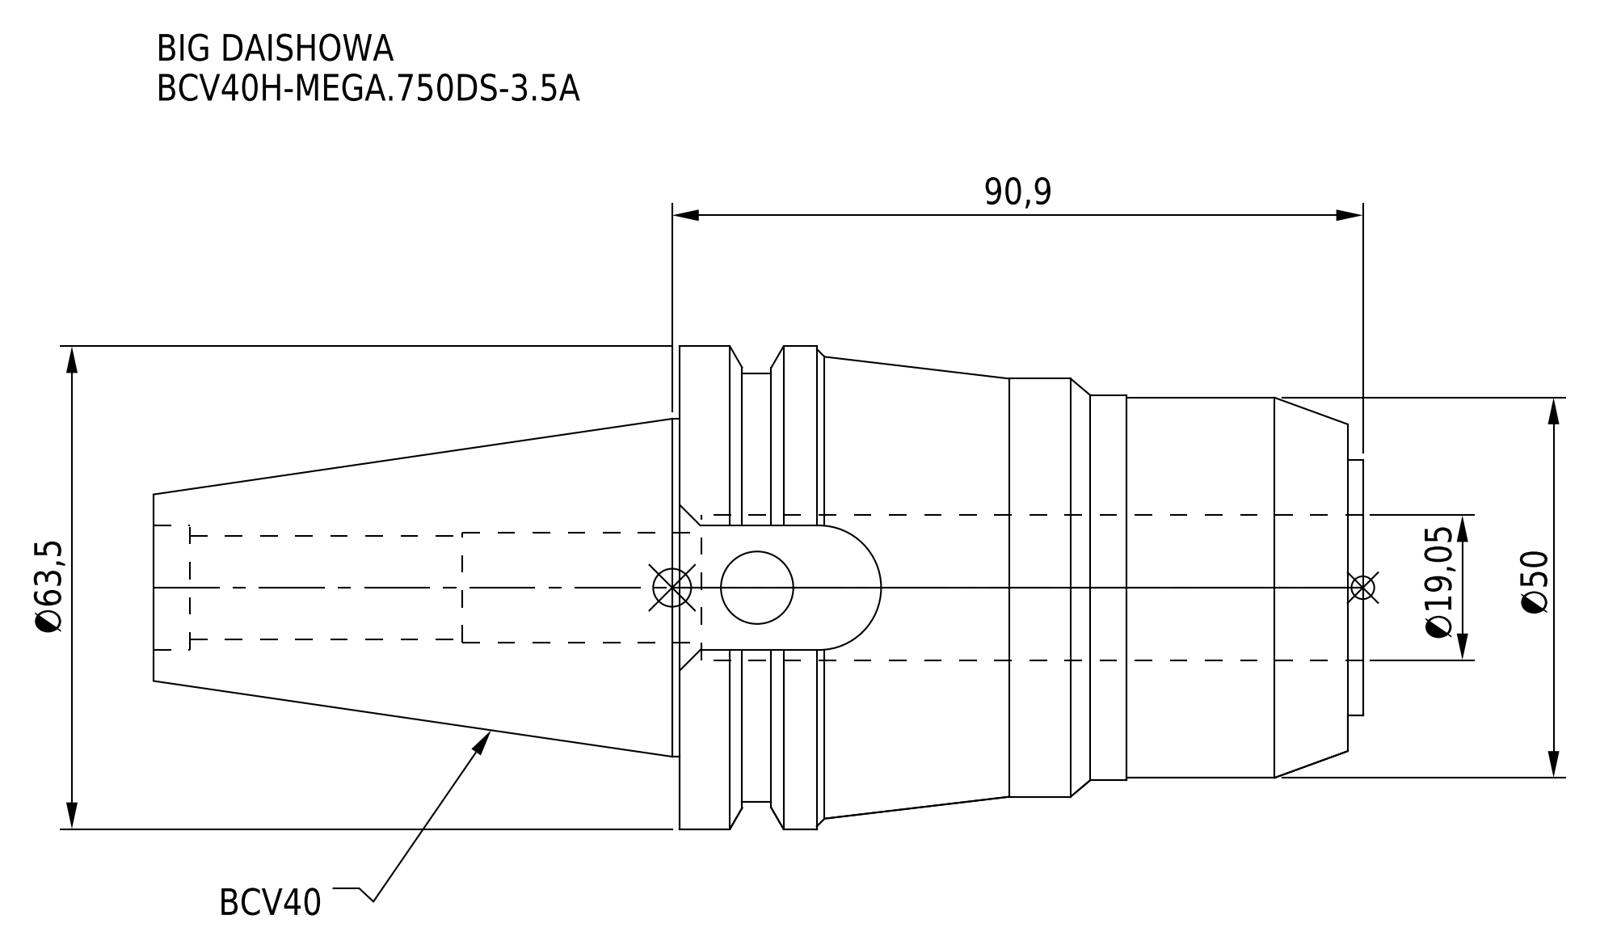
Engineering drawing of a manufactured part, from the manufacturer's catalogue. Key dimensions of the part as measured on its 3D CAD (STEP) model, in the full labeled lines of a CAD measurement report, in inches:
Part name (STEP PRODUCT): BCV40H-MEGA_750DS-3_5A
STEP written by: CREO PARAMETRIC BY PTC INC, 2016380 (AUTOMOTIVE_DESIGN)
Units: inches
Bodies: 1 solid, 69 faces (25 planar, 30 cylindrical, 14 other)
Overall size (bounding box): 6.266 × 2.5 × 2.415
Volume: 14.47 in³ · Surface area: 56.17 in²
Round holes (diameter × count): ⌀0.375 ×1, ⌀0.535 ×1, ⌀0.571 ×1, ⌀0.643 ×1, ⌀0.75 ×1
Round bosses / shafts (diameter × count): ⌀2.5 ×1, ⌀2.219 ×1, ⌀2.165 ×1, ⌀1.996 ×1, ⌀1.969 ×1, ⌀1.75 ×1, ⌀1.323 ×1
Partial cylindrical surfaces — rounded edges, fillets, slot ends (radius × count): R0.322 ×1
Main face-to-face distances: 3.539, 0.079, 3.461, 1.872, 6.266, 6.187, 2.726, 0.645, 3.425, 3.346
